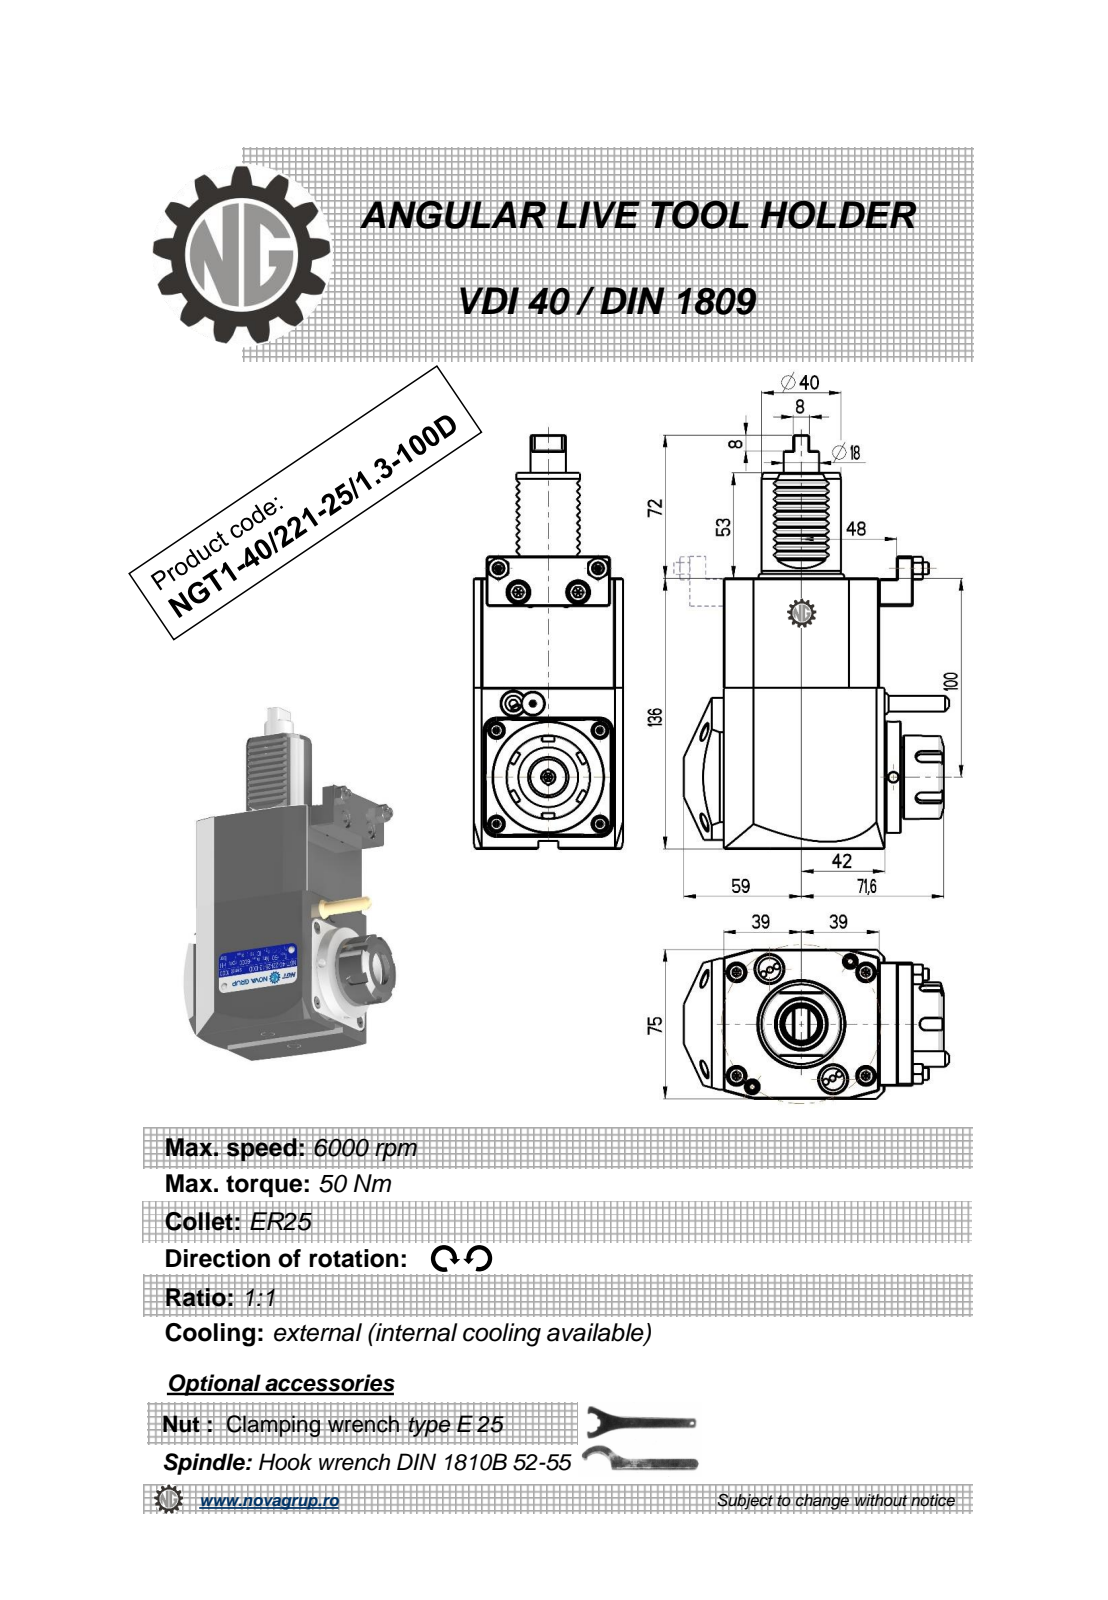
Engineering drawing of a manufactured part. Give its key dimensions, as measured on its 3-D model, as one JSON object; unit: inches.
{"part_name": "NGT1_40_221_25_1_3_100D", "step_written_by": "PRO/ENGINEER BY PARAMETRIC TECHNOLOGY CORPORATION, 2010280 (CONFIG_CONTROL_DESIGN)", "units": "inches", "bodies": {"solids": 1, "faces": 445, "planar": 208, "cylindrical": 82, "other": 155}, "overall_size": [8.189, 5.242, 2.953], "volume_in3": 59.85, "surface_area_in2": 119.3, "round_holes": [[0.197, 3], [0.118, 1], [0.799, 1]], "round_bosses_or_shafts": [[0.236, 2], [2.205, 1], [1.693, 1], [1.654, 1], [1.575, 1], [1.299, 1], [0.701, 1], [0.441, 1]], "partial_cylinders_radius": [[0.012, 20], [0.012, 10], [0.009, 6], [0.118, 5], [0.031, 2], [1.575, 1]], "face_to_face_distances": [2.953, 5.354, 3.071, 0.433, 0.551, 0.315, 3.189, 0.02, 0.236, 0.118], "hole_center_spacings": [1.611]}
